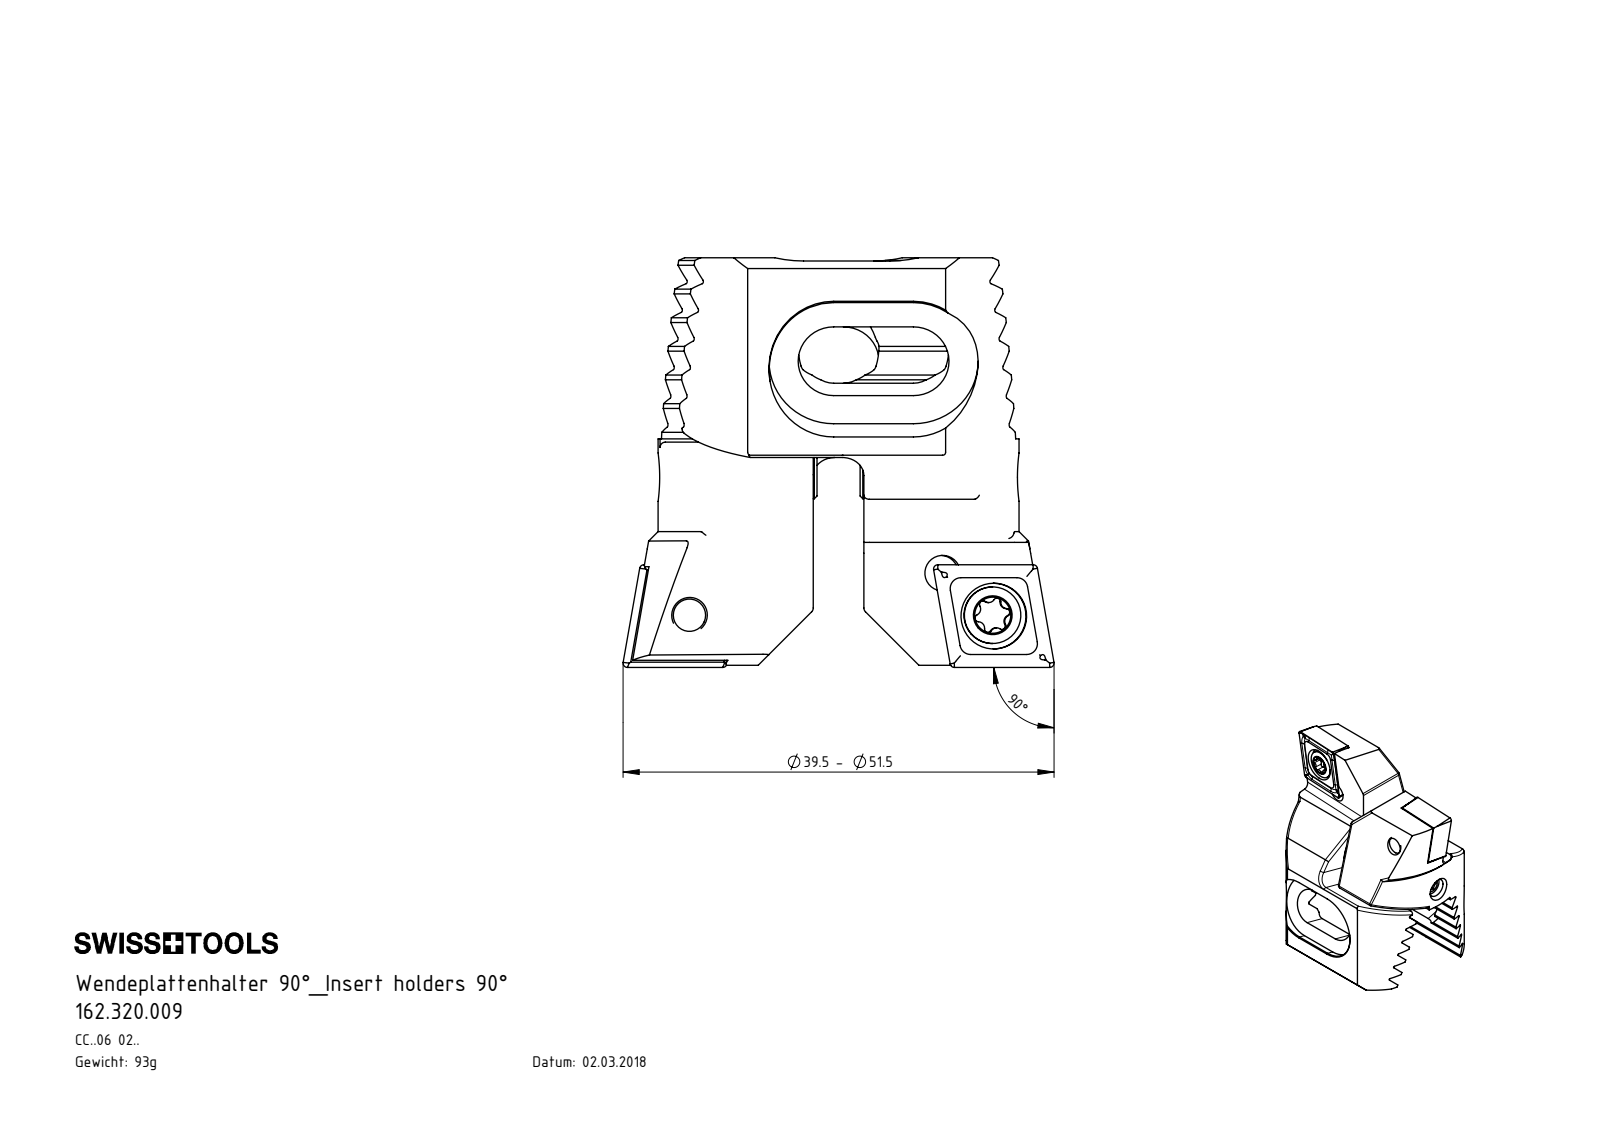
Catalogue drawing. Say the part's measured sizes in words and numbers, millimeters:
The part is named "Z32-ER3.001.013_A; 162.320.009; CCMT09T304; Z32-xxx.001.021_B (+1 more)". Its 3-D file was written by "SolidWorks 2017 (CONFIG_CONTROL_DESIGN)". It is 8 solids with 646 faces: 294 planar, 136 cylindrical and 216 other. Overall it measures 40 by 38 by 26.2 millimeters. Its volume is 11 871 cubic millimeters and its surface area 8 259 square millimeters. Round holes: 4 of diameter 3.3, 2 of diameter 1.6, 2 of diameter 4.4, 2 of diameter 6.1, 1 of diameter 2, 1 of diameter 3.5. Round bosses or shafts: 3 of diameter 4, 2 of diameter 5.25. Partial cylindrical surfaces (rounded edges, fillets, slot ends): 16 of radius 0.5, 12 of radius 0.2, 12 of radius 0.34, 12 of radius 0.59, 4 of radius 2, 4 of radius 3.3, 4 of radius 6, 4 of radius 12. The main face-to-face distances are 2.38, 4.76, 9.53, 7.15, 4.89, 11.91, 7.14, 1.27, 4.77, 2.39. The hole center spacings are 6.07, 6.19, 9, 24.23, 24.33, 28.65, 17.38, 19.27.
